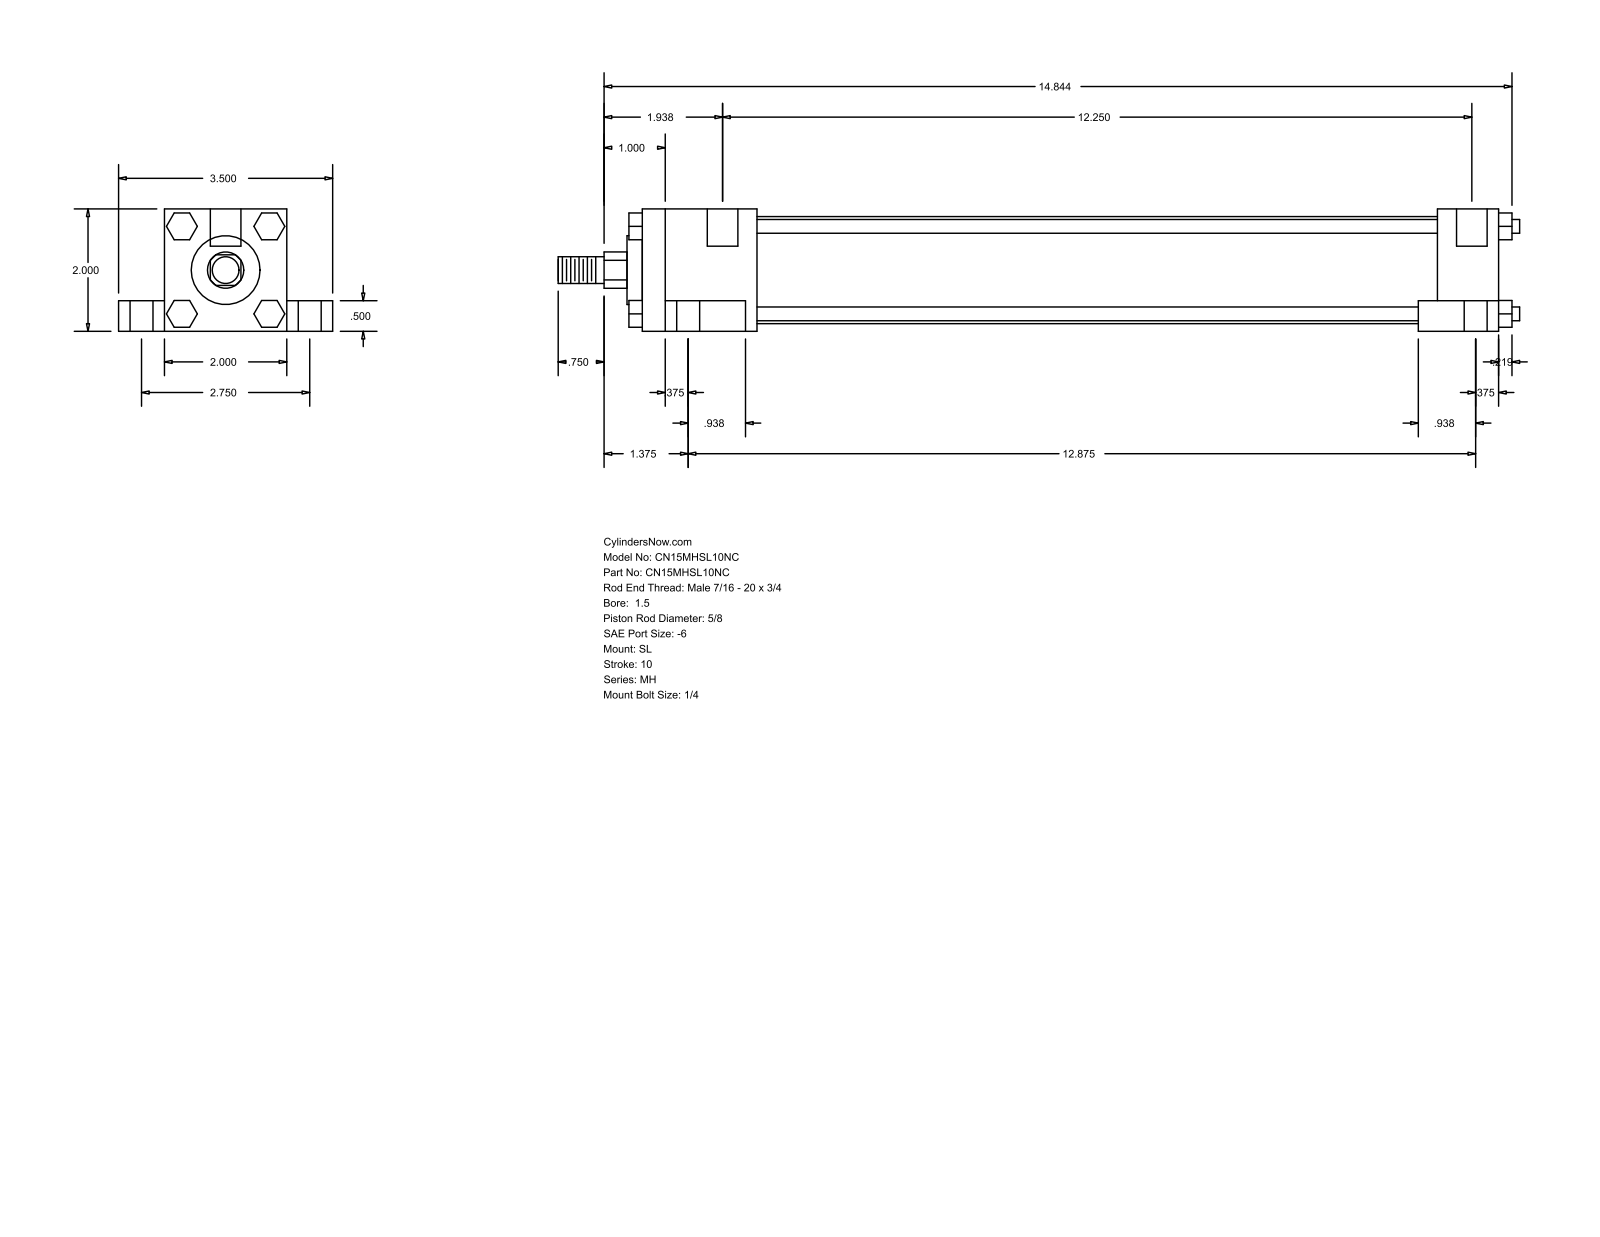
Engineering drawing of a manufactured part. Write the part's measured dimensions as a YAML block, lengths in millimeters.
part_name: "MH_SL__0150_0.625"
step_written_by: "GSSL Pune (CONFIG_CONTROL_DESIGN)"
units: millimeters
bodies: {solids: 0, faces: 148, planar: 112, cylindrical: 36, other: 0}
overall_size: [399.26, 88.9, 50.8]
round_holes:
  - {diameter: 5.56, count: 4}
  - {diameter: 9.53, count: 4}
  - {diameter: 15.88, count: 4}
  - {diameter: 12.7, count: 2}
round_bosses_or_shafts:
  - {diameter: 5.71, count: 4}
  - {diameter: 44.45, count: 1}
  - {diameter: 28.57, count: 1}
  - {diameter: 15.88, count: 1}
  - {diameter: 11.11, count: 1}
partial_cylinders:
  - {radius: 7.54, count: 1}
face_to_face_distances: [50.8, 38.1, 19.05, 12.7, 69.85, 355.6, 9.52, 33.34, 312.74, 330.19]
hole_center_spacings: [34.96, 36.65, 37.73, 69.84, 314.32, 314.68, 317.83, 327.03]
